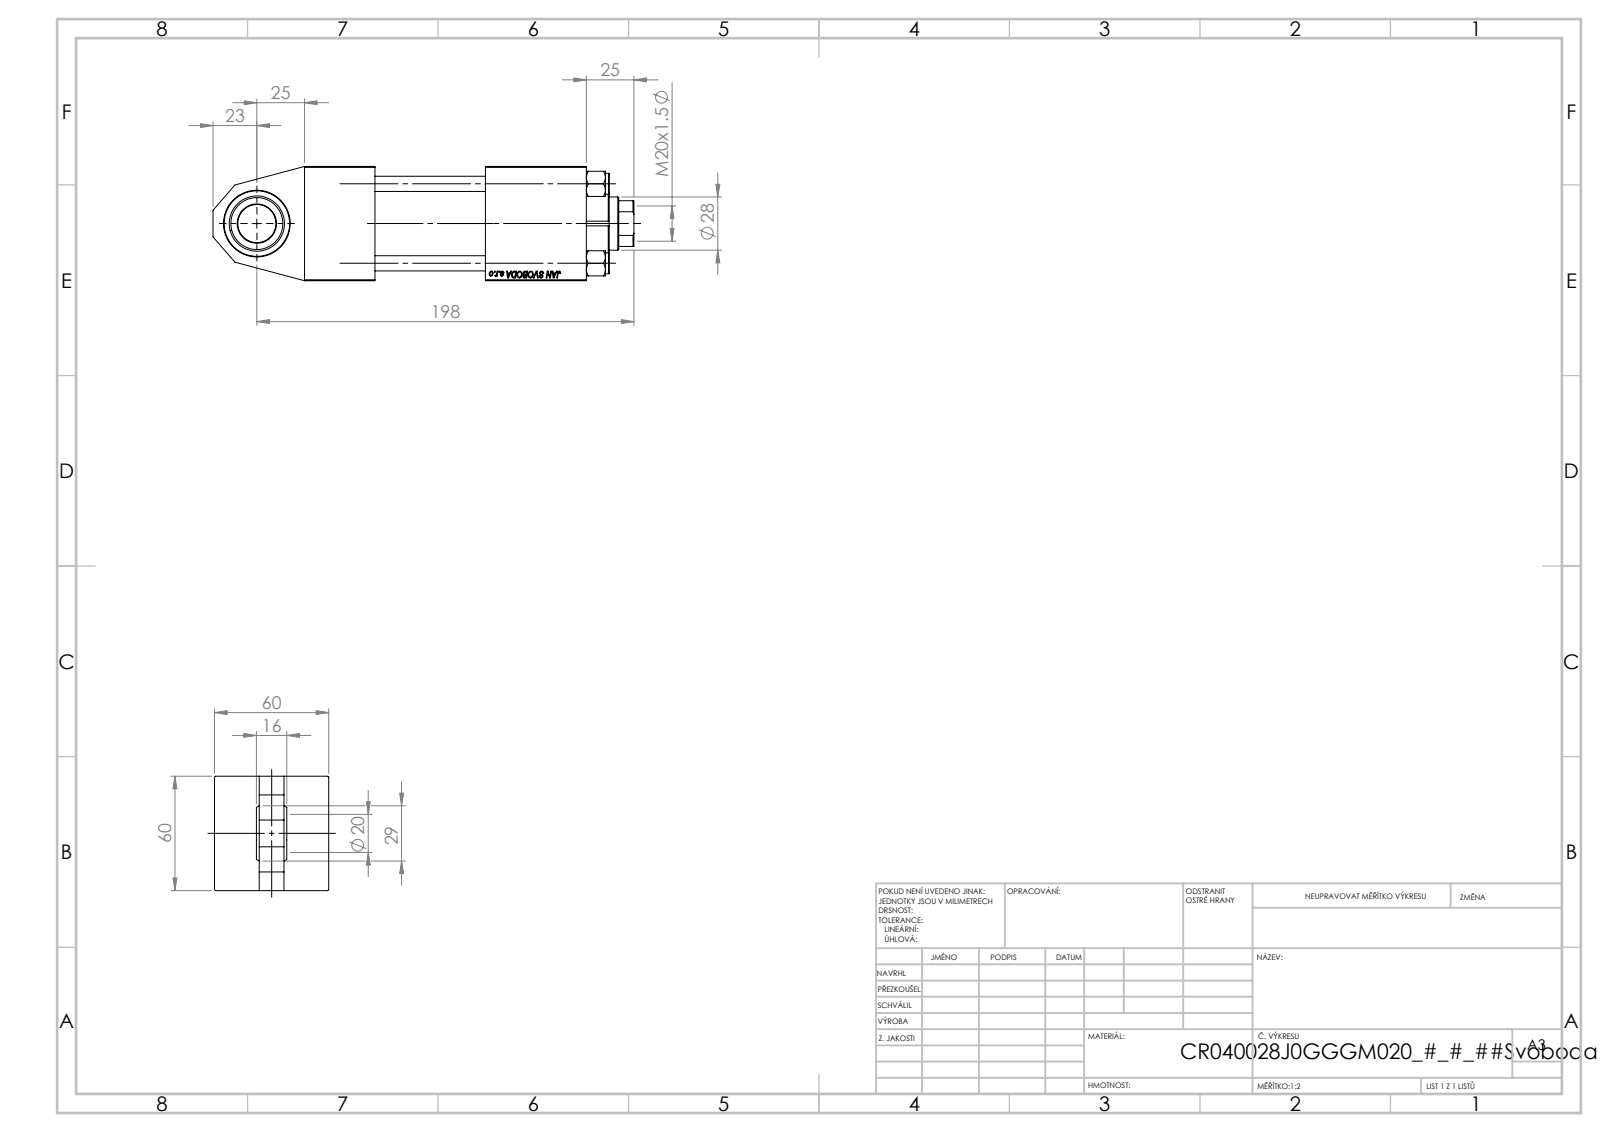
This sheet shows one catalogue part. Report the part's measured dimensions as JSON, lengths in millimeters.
{"part_name": "V215CR_TYCINKA_J; NUT_M5_J; V215CR_J_VNITRNI_KROUZEK; V215_VC_A (+2 more)", "step_written_by": "SolidWorks 2019 (CONFIG_CONTROL_DESIGN)", "units": "millimeters", "bodies": {"solids": 12, "faces": 1147, "planar": 519, "cylindrical": 88, "other": 540}, "overall_size": [221, 60, 60], "volume_mm3": 451157, "surface_area_mm2": 120726, "round_holes": [[8, 4], [2.5, 2], [7, 2], [16.66, 2], [24, 2], [18.5, 1], [20, 1], [28, 1], [31, 1], [35, 1], [40, 1], [45, 1]], "round_bosses_or_shafts": [[11, 4], [46, 1], [42, 1]], "partial_cylinders_radius": [[13.5, 1]], "face_to_face_distances": [60, 36.5, 23.5, 37, 53, 58, 95, 148, 111, 13], "hole_center_spacings": [20.85, 29.49, 41.7, 46.53, 20.75, 58.97, 41.5, 92.5]}
